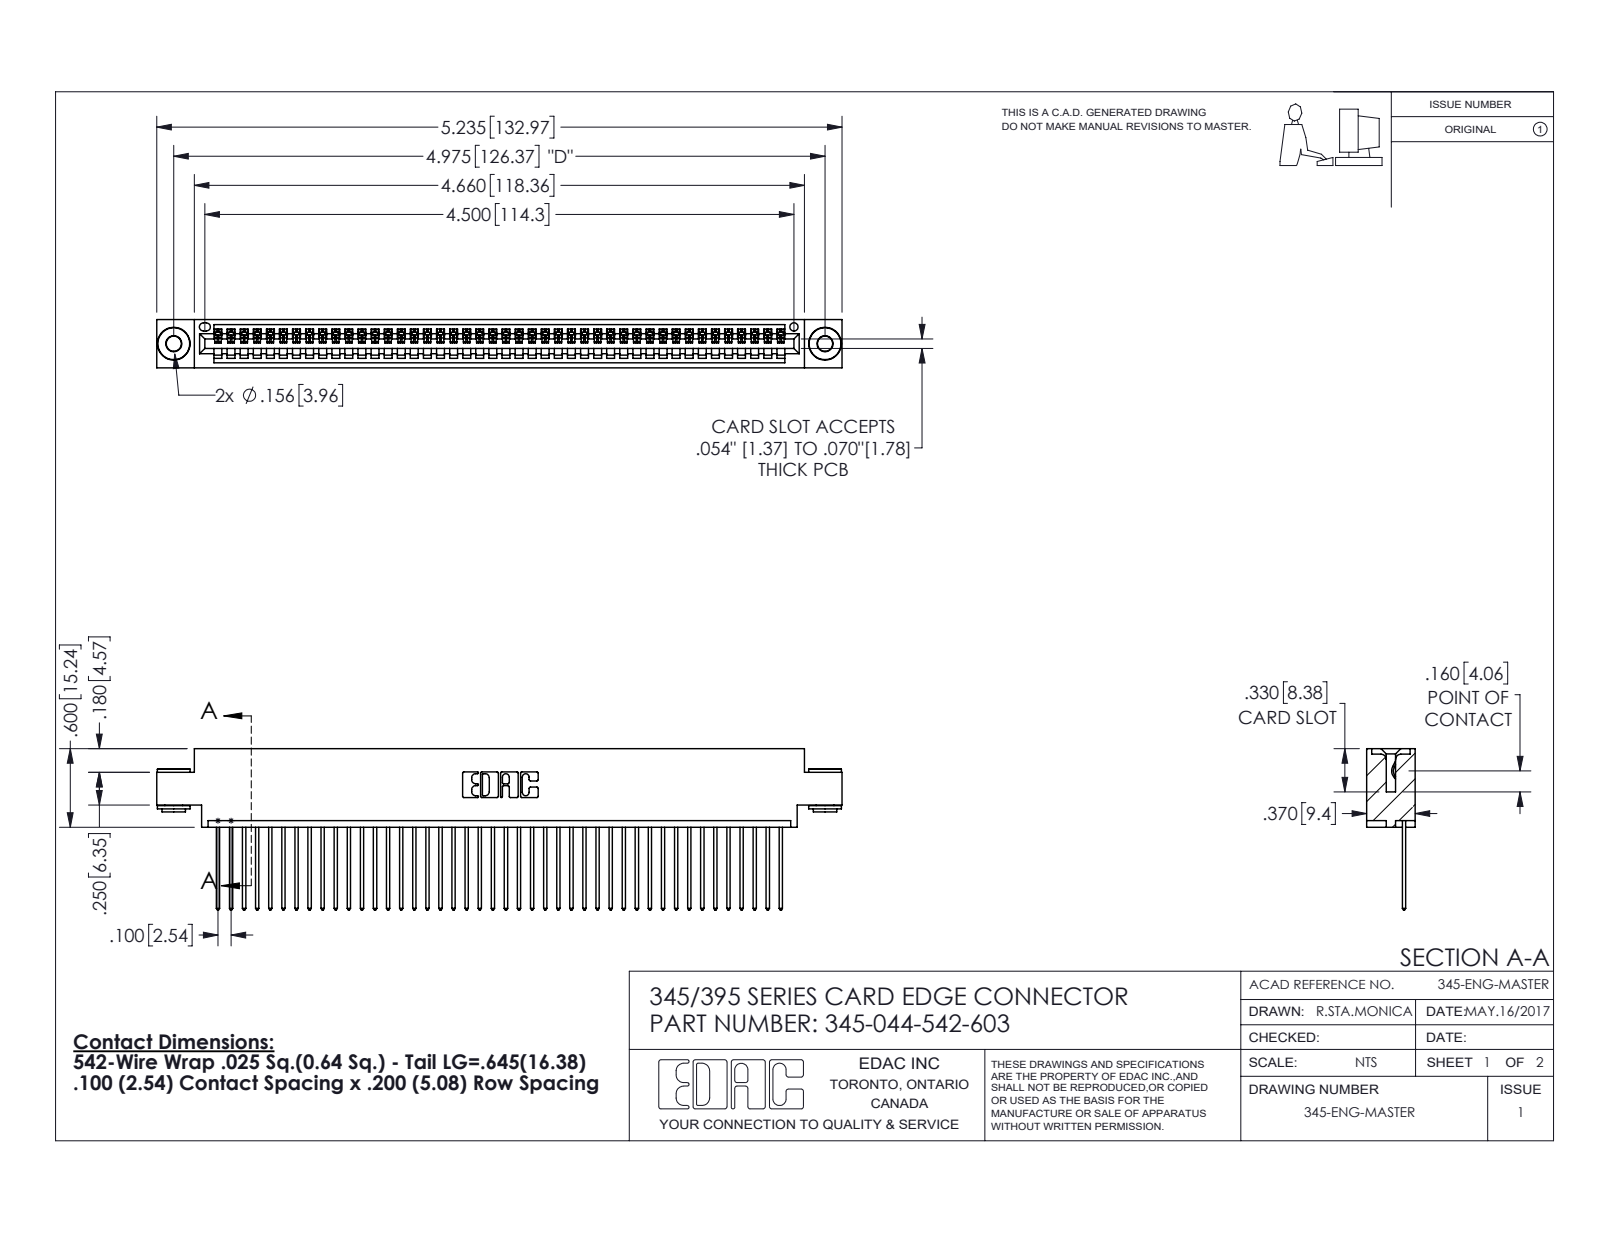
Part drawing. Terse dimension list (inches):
name: 345-292-001_345-293-142; 345 Part_0.170 Offset - 0.156 Dia-TH; 345-044-542-603; 345-250-002_345-250-002-102
written by: SolidWorks 2016 (CONFIG_CONTROL_DESIGN)
unit: in
bodies: 47 solids, 2720 faces (1854 planar, 858 cylindrical, 8 other)
size: 5.235 × 1.232 × 0.37
volume: 0.772 in³; area: 27.59 in²
holes: 2× ⌀0.116, 2× ⌀0.156, 1× ⌀0.064
bosses: 2× ⌀0.25, 2× ⌀0.18, 2× ⌀0.136
rounds: 88× R0.006, 88× R0.01, 22× R0.01, 6× R0.007, 6× R0.031, 3× R0.026, 2× R0.031, 2× R0.04
face distances: 0.072, 0.298, 0.37, 0.098, 0.272, 0.025, 0.2, 0.225, 0.175, 0.149
hole spacings: 0.27, 4.739, 4.975
